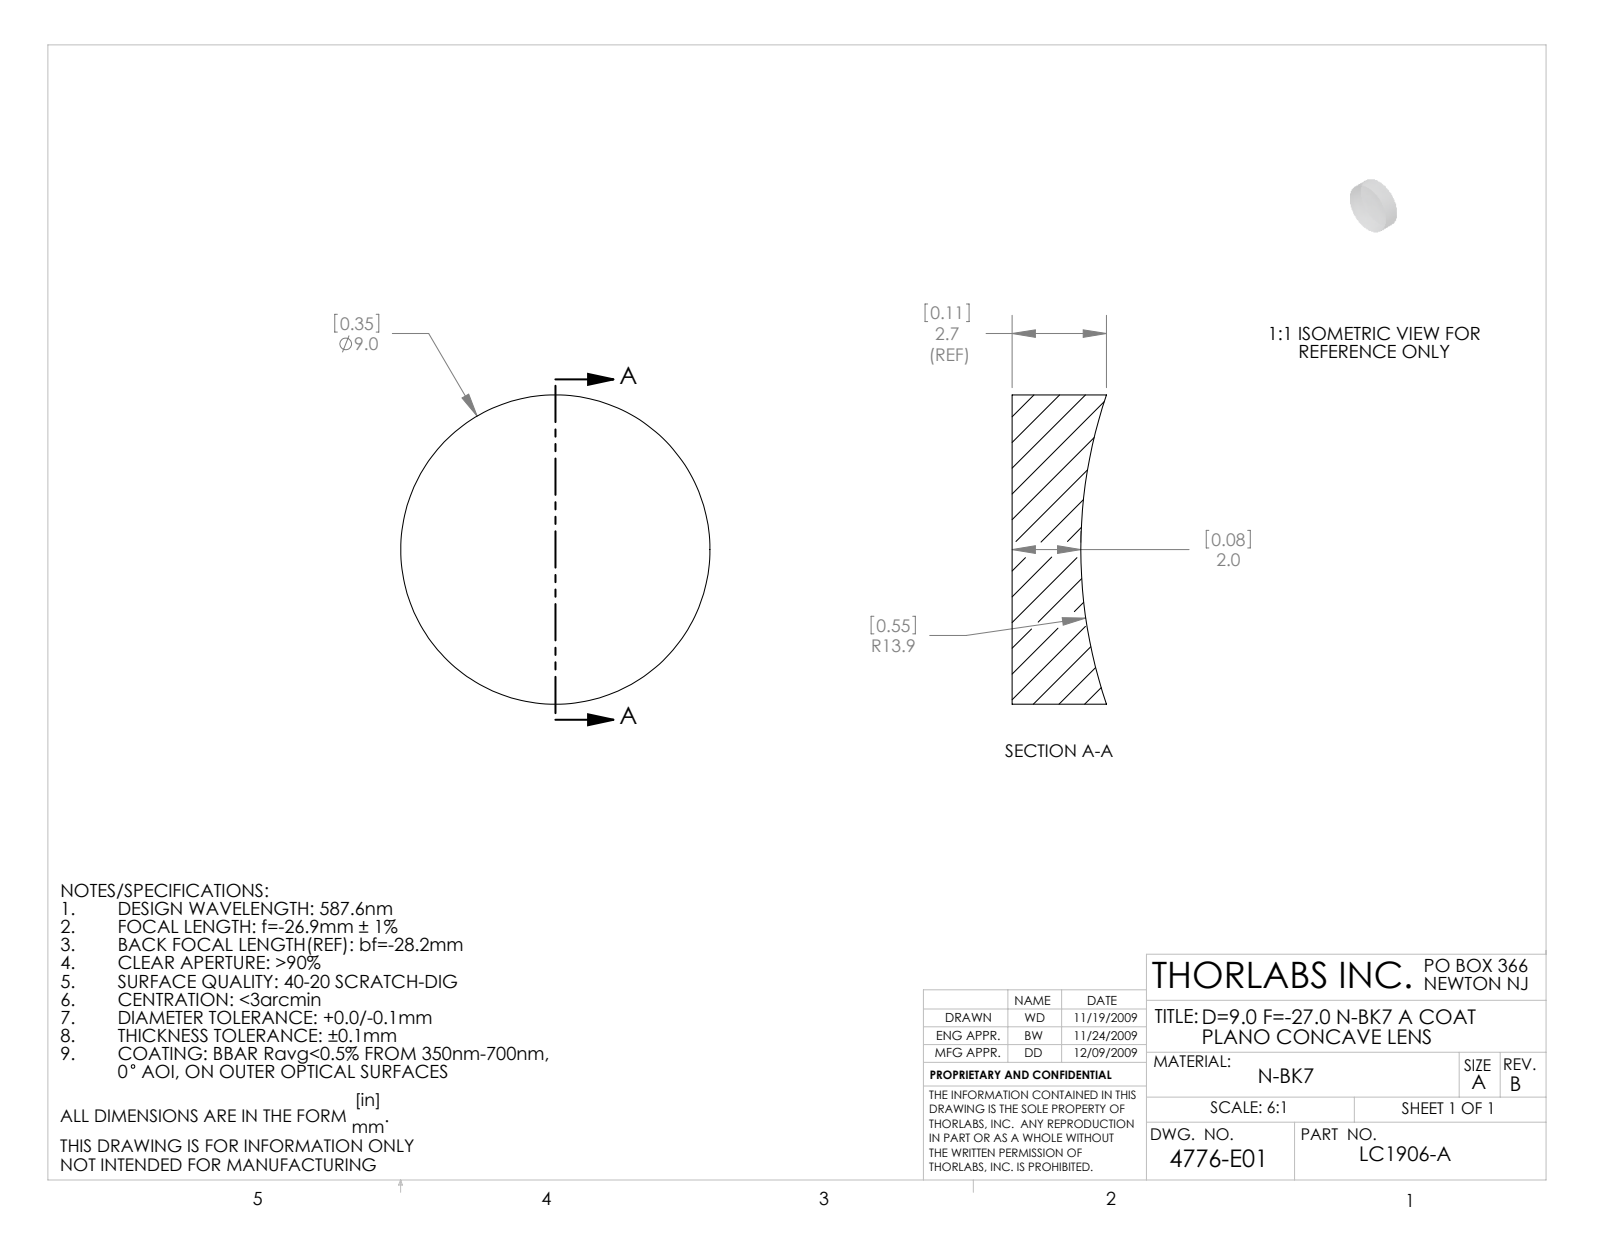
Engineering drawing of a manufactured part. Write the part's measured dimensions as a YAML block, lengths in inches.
part_name: "4776-E0W"
step_written_by: "SolidWorks 2009 (AUTOMOTIVE_DESIGN)"
units: inches
bodies: {solids: 1, faces: 5, planar: 1, cylindrical: 2, other: 2}
overall_size: [0.354, 0.354, 0.108]
volume: 0.009
surface_area: 0.321
round_bosses_or_shafts:
  - {diameter: 0.354, count: 1}
